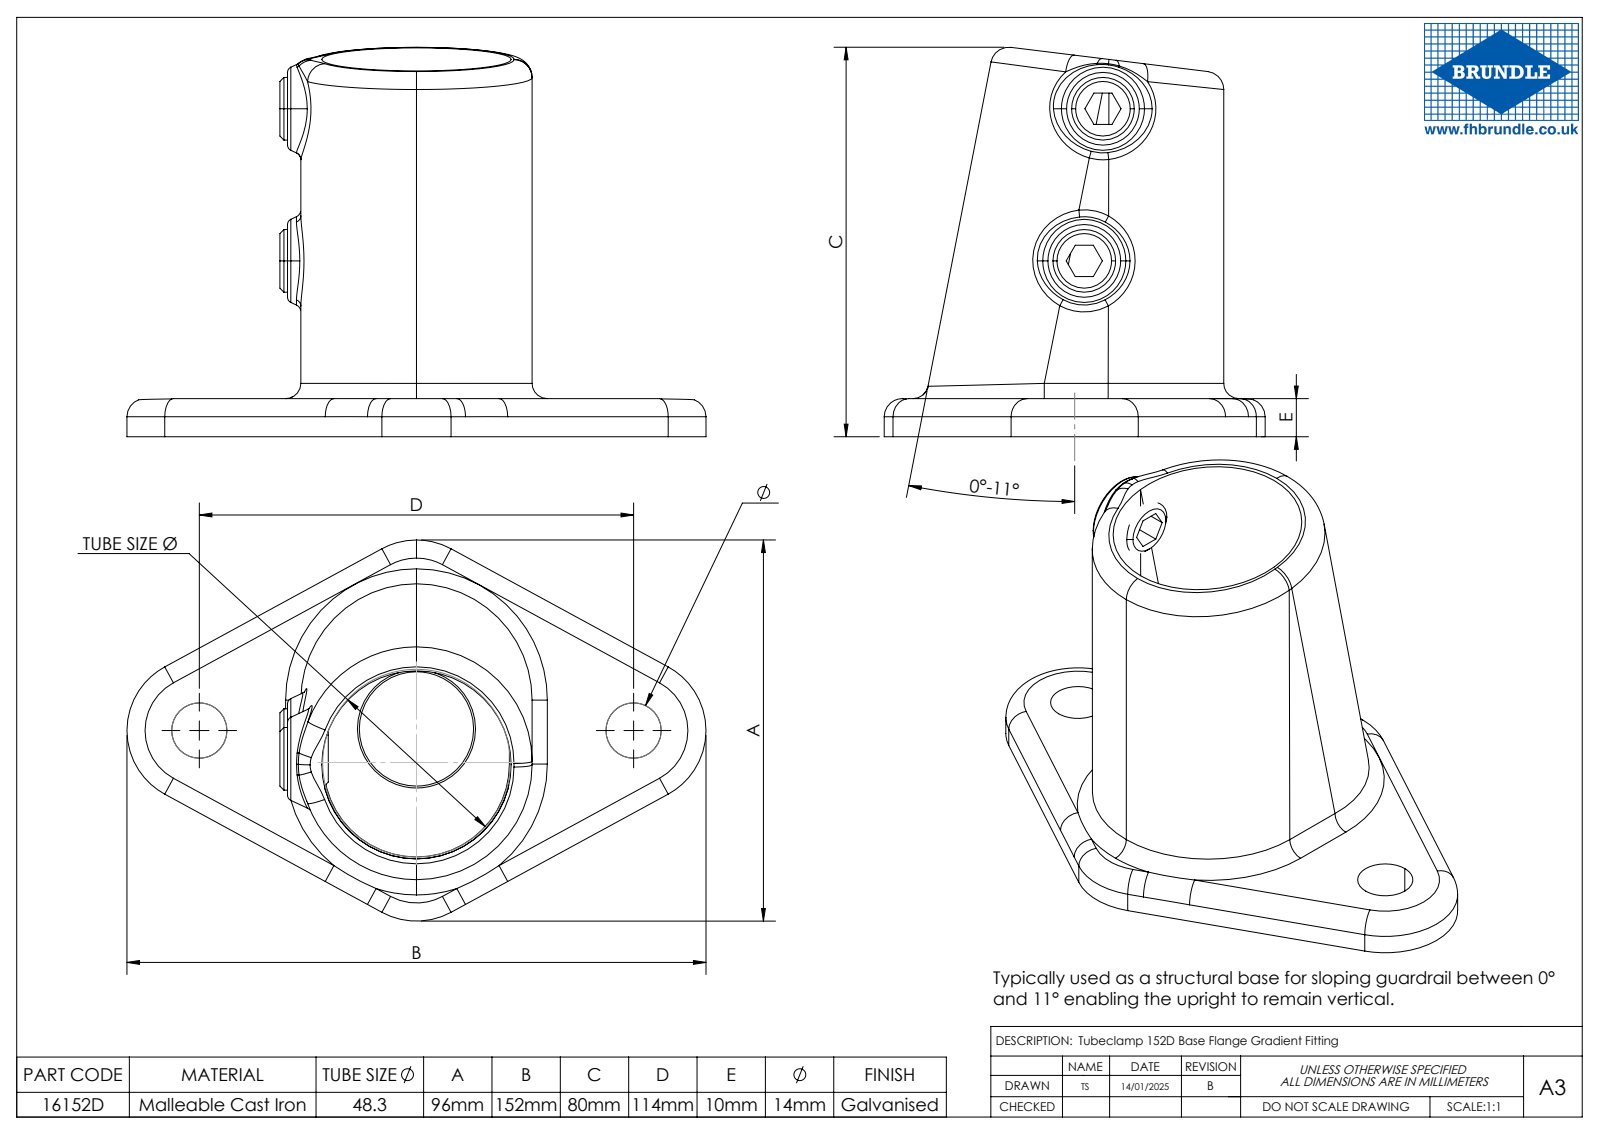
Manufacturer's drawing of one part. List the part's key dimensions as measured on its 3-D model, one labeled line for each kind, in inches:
Part name (STEP PRODUCT): 16152D
STEP written by: SolidWorks 2018 (CONFIG_CONTROL_DESIGN)
Units: inches
Bodies: 3 solids, 118 faces (0 planar, 0 cylindrical, 118 other)
Overall size (bounding box): 5.984 × 4.023 × 3.937
Volume: 10.41 in³ · Surface area: 91.01 in²
